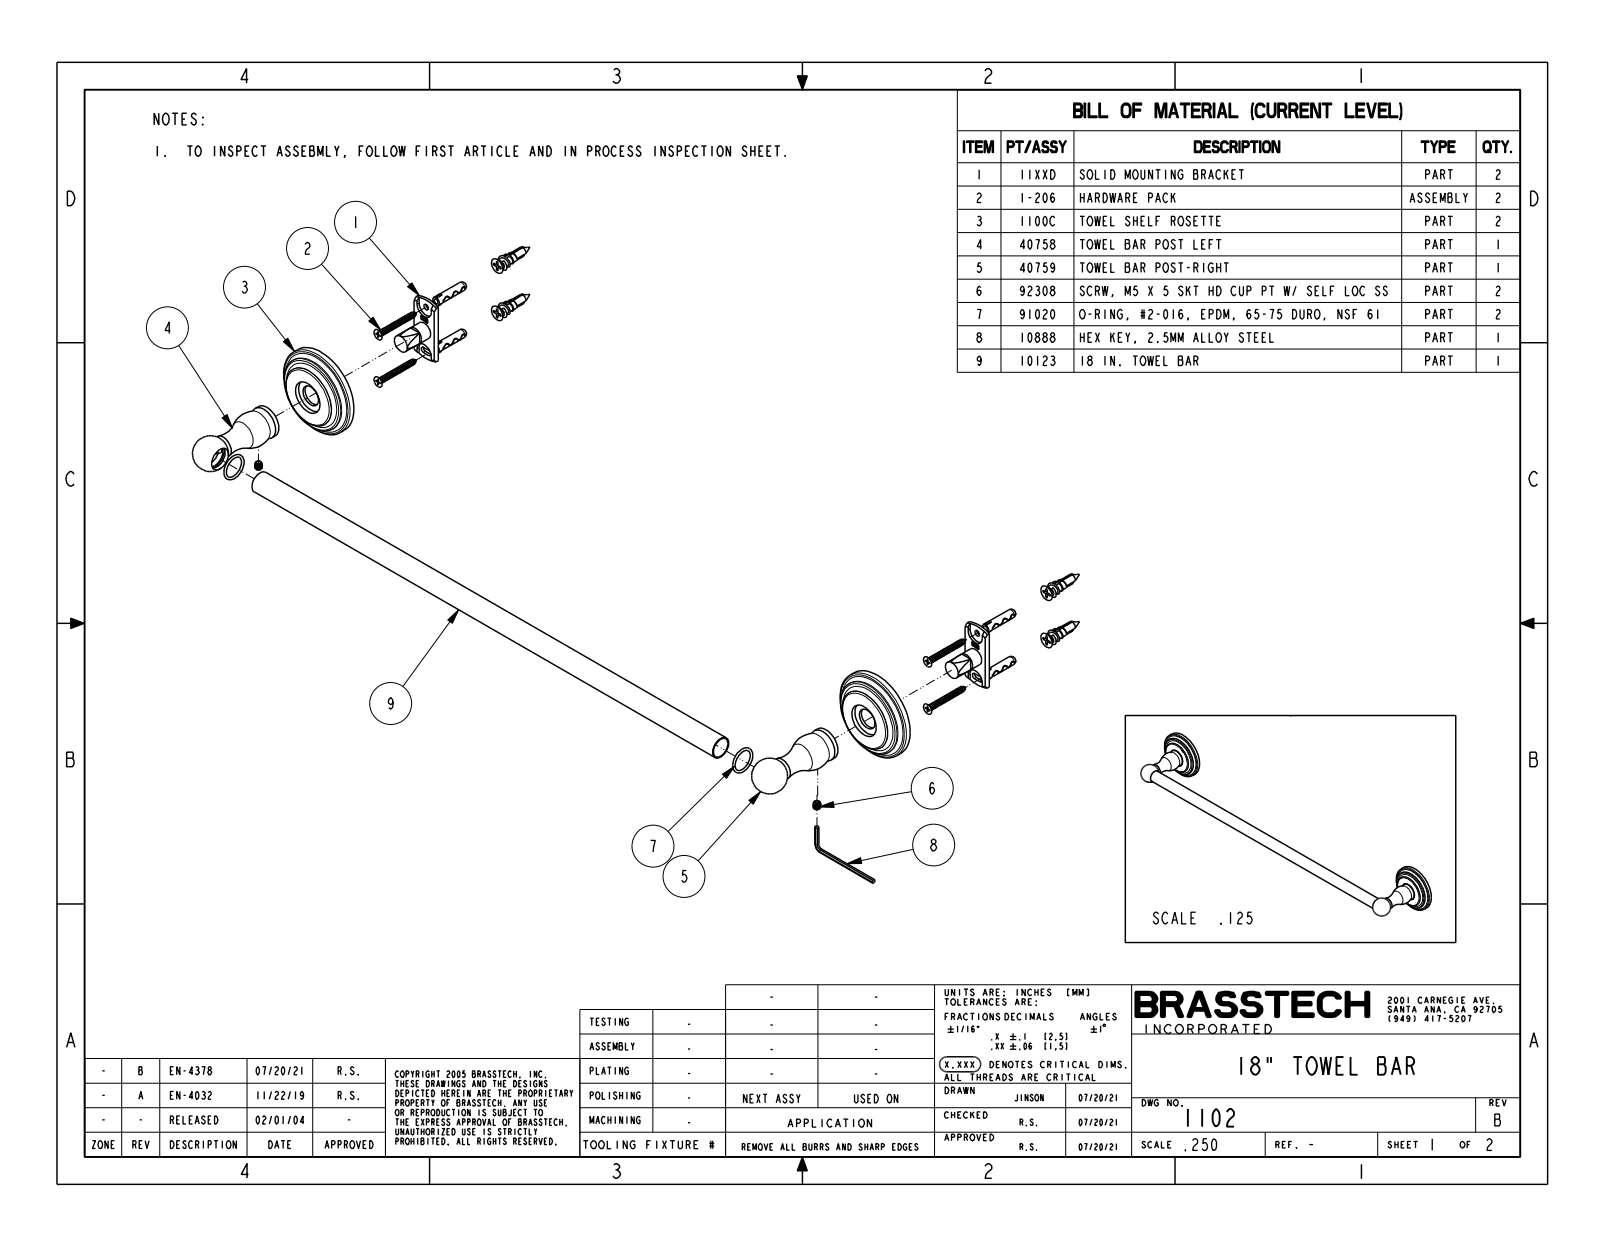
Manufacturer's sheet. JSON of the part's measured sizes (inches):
{"part_name": "1102", "step_written_by": "CREO PARAMETRIC BY PTC INC, 2018400 (CONFIG_CONTROL_DESIGN)", "units": "inches", "bodies": {"solids": 1, "faces": 72, "planar": 10, "cylindrical": 22, "other": 40}, "overall_size": [20.56, 3.075, 2.56], "volume_in3": 11.83, "surface_area_in2": 72.62, "round_holes": [[0.65, 1]], "round_bosses_or_shafts": [[2.56, 2], [2.182, 2], [1.748, 2], [0.928, 2], [0.625, 1]], "face_to_face_distances": [0.512, 0.362, 0.15, 0.189, 0.173, 0.323, 17.51]}
